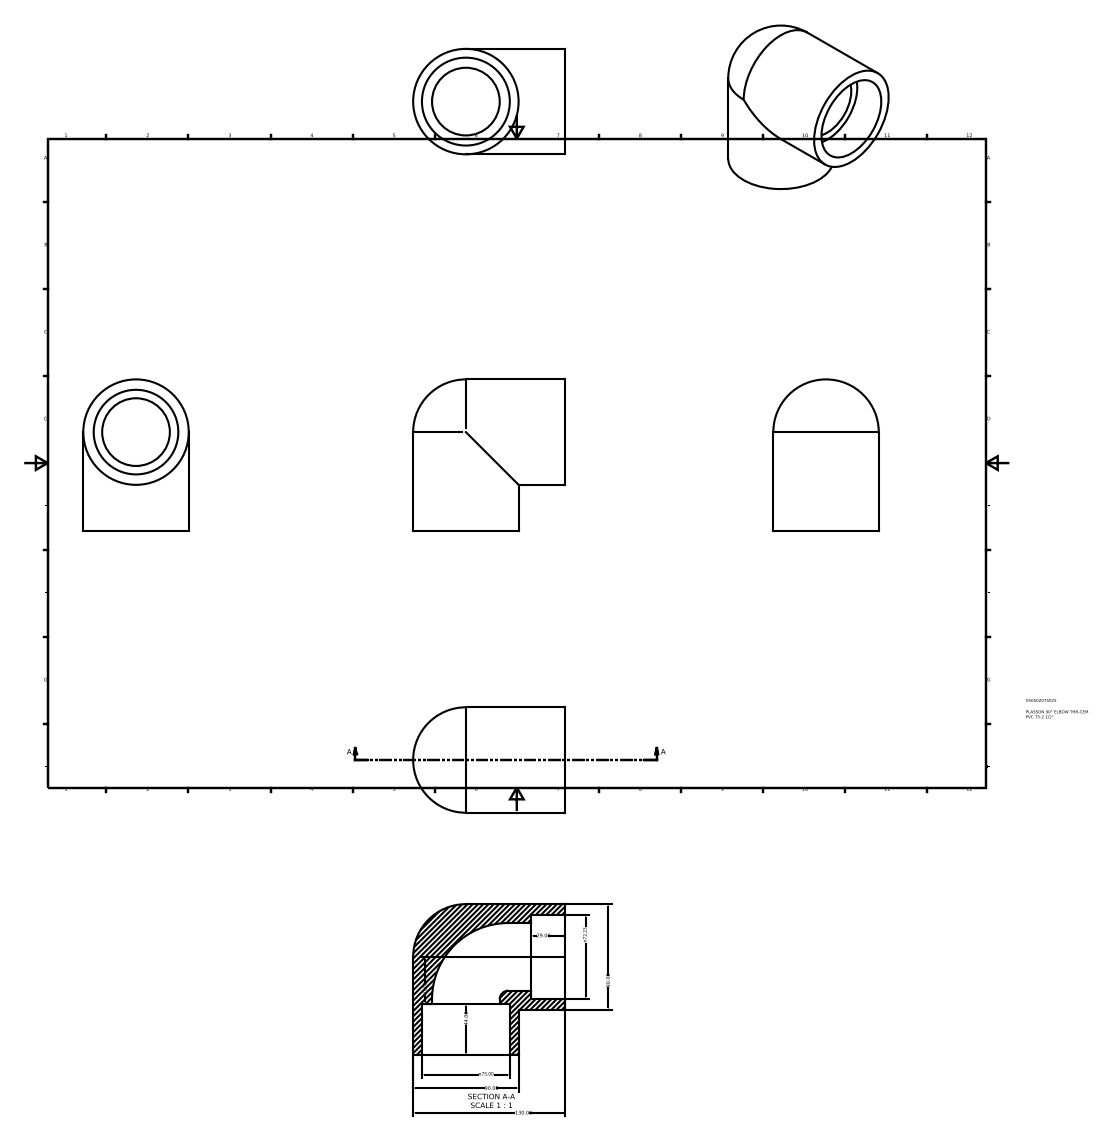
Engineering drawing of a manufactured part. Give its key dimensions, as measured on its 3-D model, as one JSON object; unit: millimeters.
{"part_name": "050502075025", "step_written_by": "Autodesk Inventor 2015 (AUTOMOTIVE_DESIGN)", "units": "millimeters", "bodies": {"solids": 1, "faces": 12, "planar": 4, "cylindrical": 6, "other": 2}, "overall_size": [130, 129, 90], "volume_mm3": 524772, "surface_area_mm2": 85085, "round_holes": [[57.78, 2], [72.23, 1], [75, 1]], "round_bosses_or_shafts": [[90, 2]], "face_to_face_distances": [44, 29]}
